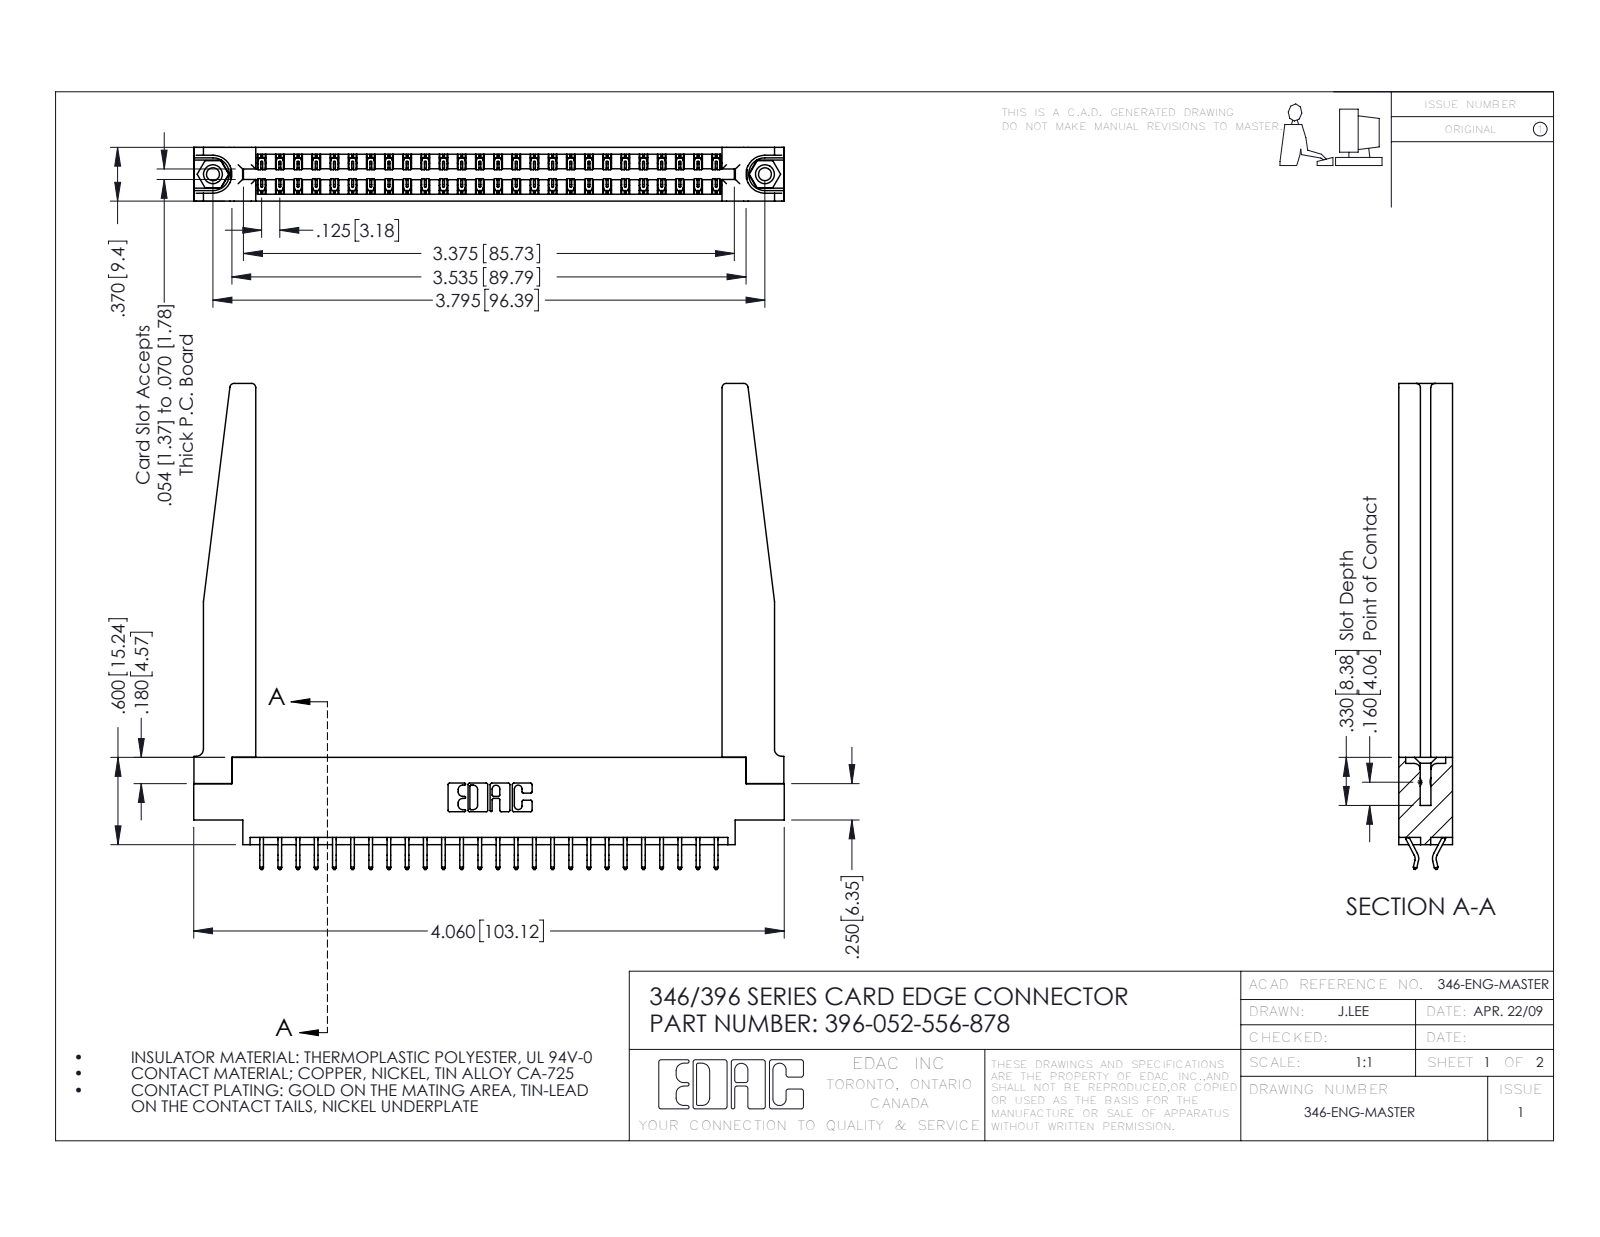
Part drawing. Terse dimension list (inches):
name: 345-250-001_345-250-001-102; 346 Part_0.170 Offset - 0.156 Dia-TH; 345-292-001_556 Tail; 396-052-556-878 (+1 more)
written by: SolidWorks 2016 (CONFIG_CONTROL_DESIGN)
unit: in
bodies: 57 solids, 3376 faces (2250 planar, 1074 cylindrical, 52 other)
size: 4.06 × 3.34 × 0.37
volume: 1.018 in³; area: 30.77 in²
holes: 2× ⌀0.089, 2× ⌀0.125, 2× ⌀0.156, 1× ⌀0.064
bosses: 2× ⌀0.155
rounds: 78× R0.006, 22× R0.01, 8× R0.03, 6× R0.007, 6× R0.031, 4× R0.05, 3× R0.026, 2× R0.01
face distances: 0.37, 0.048, 0.322, 0.072, 0.148, 0.15, 0.25, 0.025, 0.298, 0.275
hole spacings: 0.246, 3.587, 3.795
